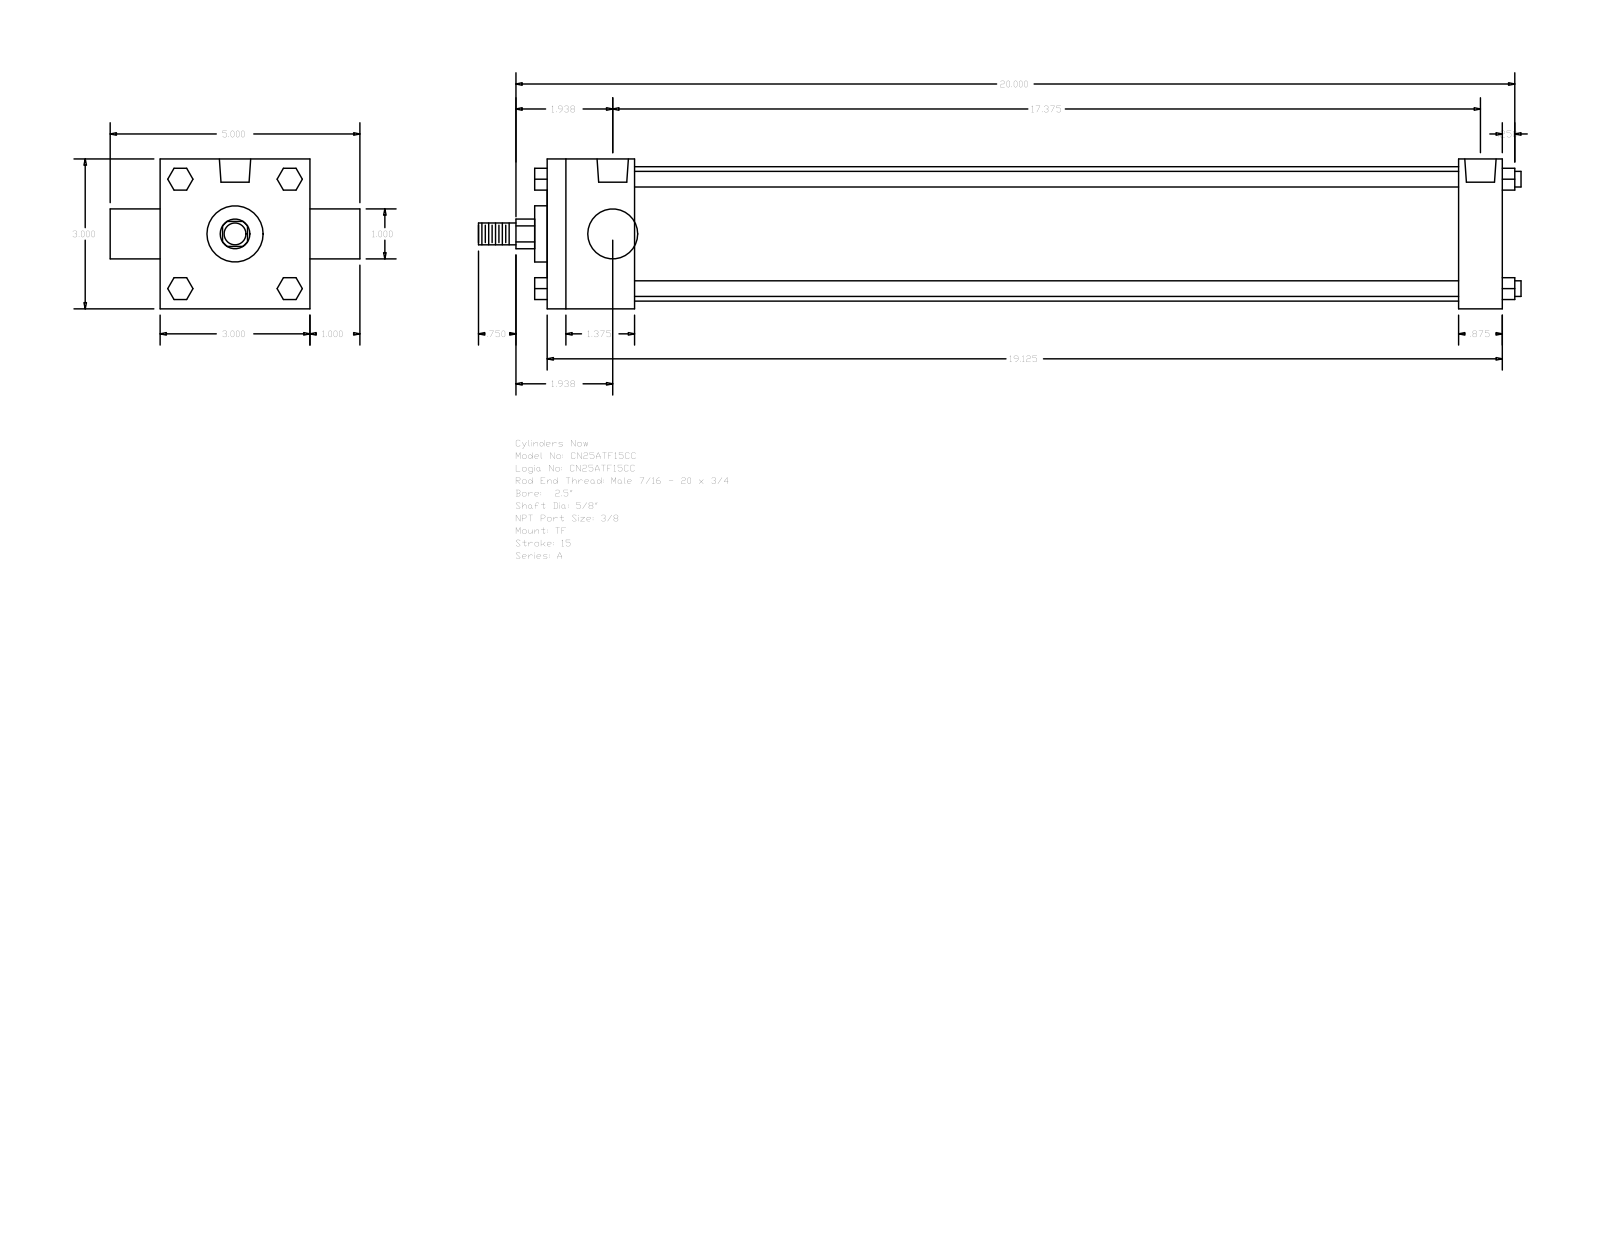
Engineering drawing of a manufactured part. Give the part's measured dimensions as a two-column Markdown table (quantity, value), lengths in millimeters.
| quantity | value |
| --- | --- |
| part name | A_TF__0250_0.625 |
| STEP written by | GSSL Pune (CONFIG_CONTROL_DESIGN) |
| units | millimeters |
| bodies | 0 solids, 120 faces (92 planar, 28 cylindrical, 0 other) |
| overall size | 530.23 × 127 × 76.2 |
| round holes (diameter × count) | 5.56 × 3, 15.93 × 2 |
| round bosses / shafts (diameter × count) | 7.94 × 4, 68.33 × 1, 28.57 × 1, 25.4 × 1, 15.88 × 1, 11.11 × 1 |
| partial cylindrical surfaces (radius × count) | 7.54 × 1 |
| main face-to-face distances | 76.2, 485.77, 44.45, 463.55, 419.1, 441.32, 22.22, 25.4, 101.6, 6.35 |
| hole center spacings | 2.38, 443.71, 441.33, 446.09 |
